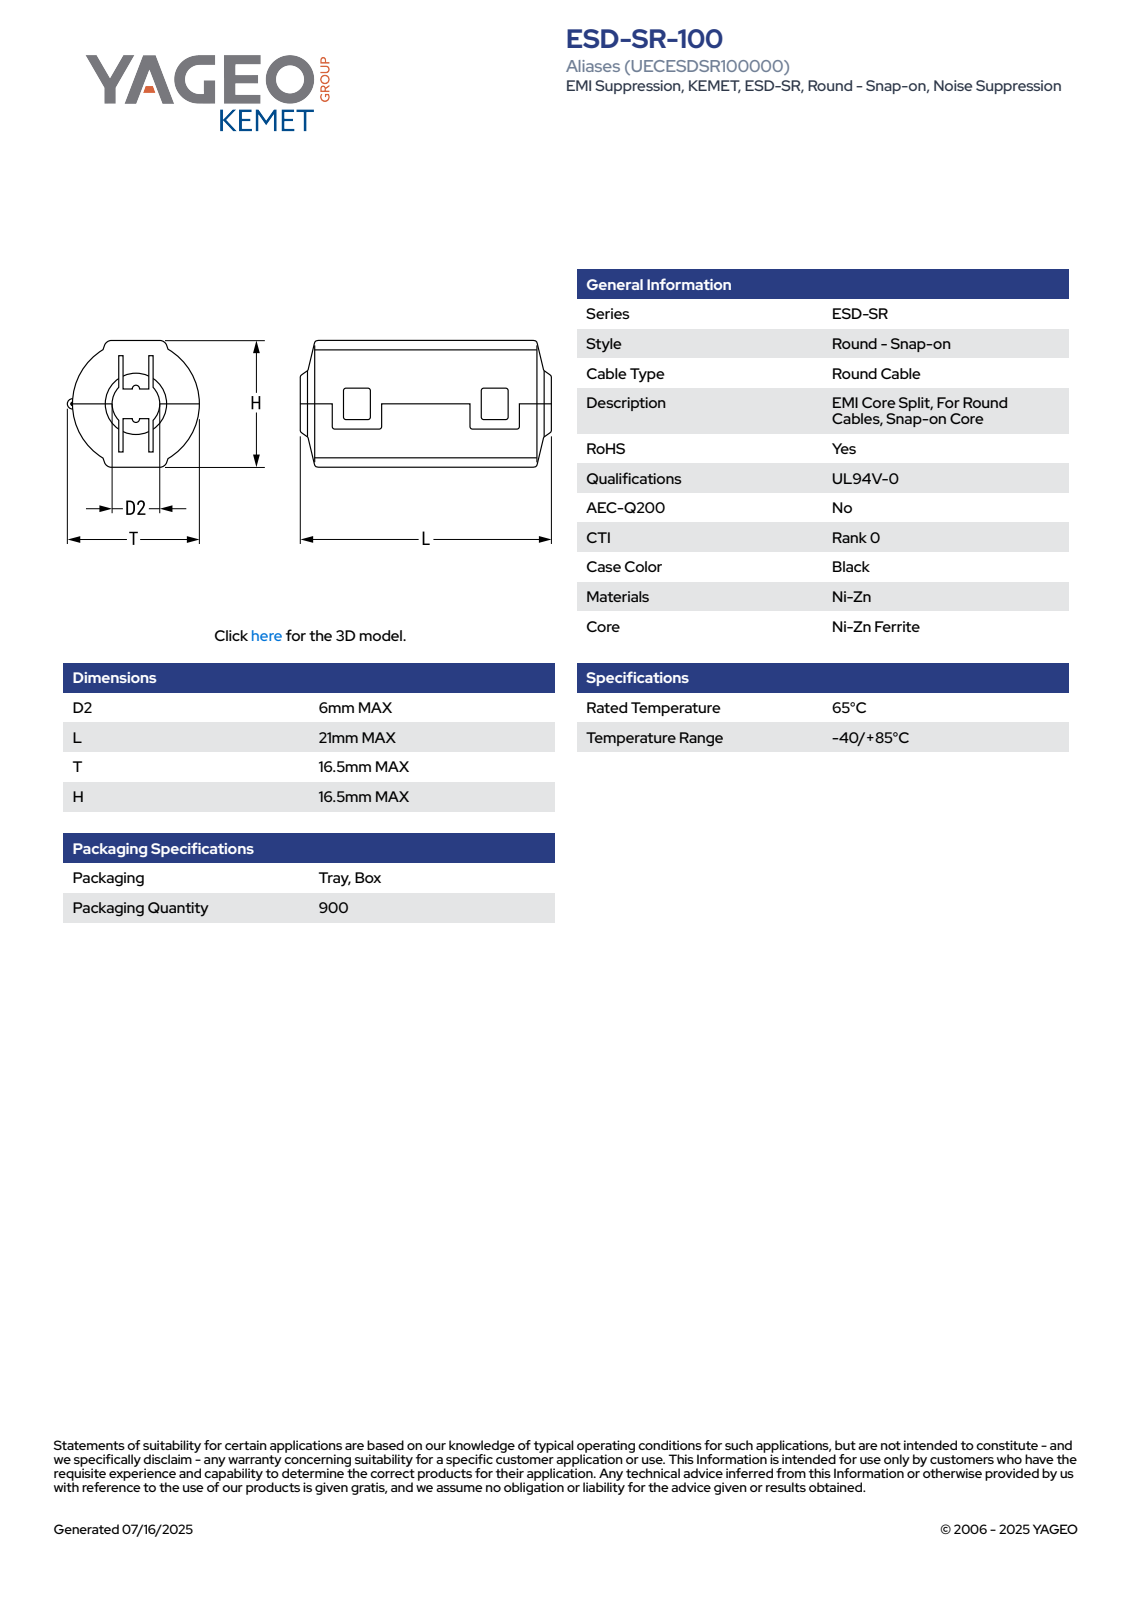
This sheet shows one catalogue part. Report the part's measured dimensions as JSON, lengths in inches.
{"part_name": "EC_ESDSR_D26L21T16.5H16.5", "step_written_by": "SolidWorks 2014 (AUTOMOTIVE_DESIGN)", "units": "inches", "bodies": {"solids": 1, "faces": 92, "planar": 72, "cylindrical": 6, "other": 14}, "overall_size": [0.827, 0.65, 0.65], "volume_in3": 0.237, "surface_area_in2": 2.83, "partial_cylinders_radius": [[0.126, 2], [0.325, 1]], "face_to_face_distances": [0.65, 0.243, 0.407, 0.165, 0.481, 0.089, 0.738, 0.827, 0.165, 0.316]}
